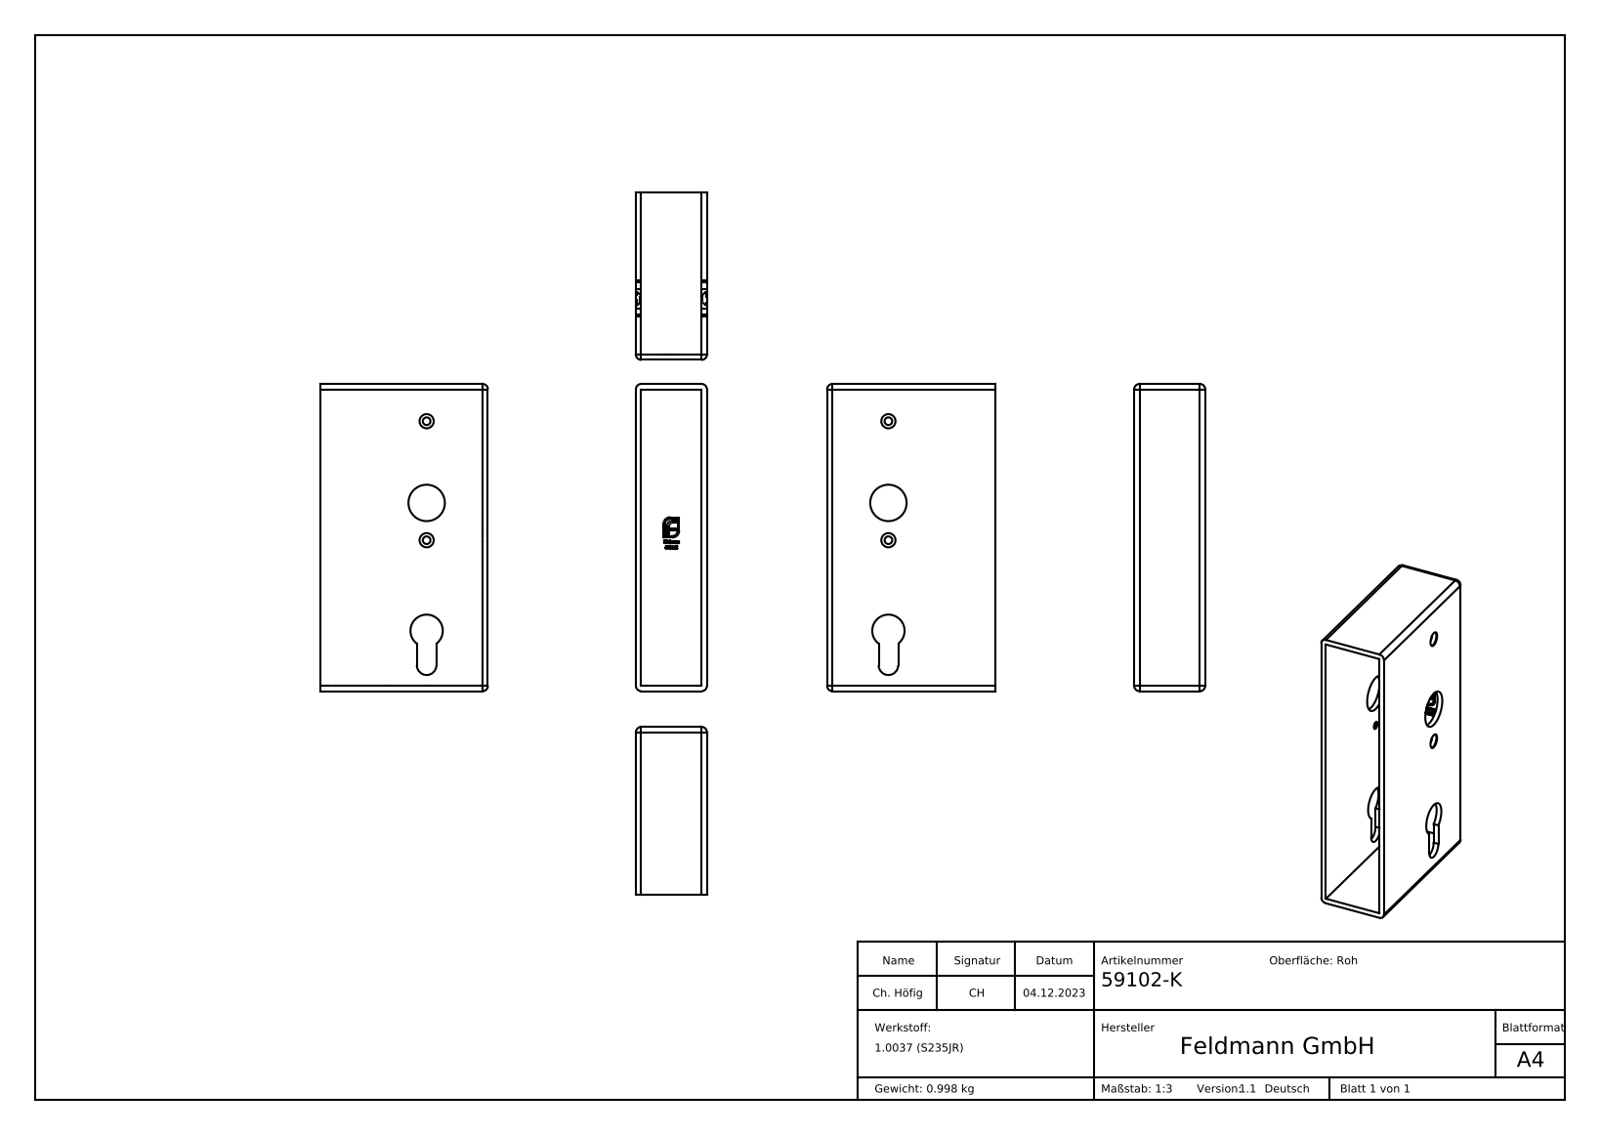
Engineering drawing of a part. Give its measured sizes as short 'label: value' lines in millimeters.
name: 59102-K
written by: SolidWorks 2018 (CONFIG_CONTROL_DESIGN)
unit: mm
bodies: 1 solid, 278 faces (148 planar, 22 cylindrical, 108 other)
size: 173 × 94.5 × 40
volume: 127 953 mm³; area: 87 756 mm²
holes: 2× ⌀4.3, 2× ⌀8, 1× ⌀20.5
rounds: 8× R3, 1× R5.5, 1× R9.1
face distances: 3, 37, 40, 34, 170, 173, 167, 94.5, 91.5, 54.5
hole spacings: 21, 46, 67
